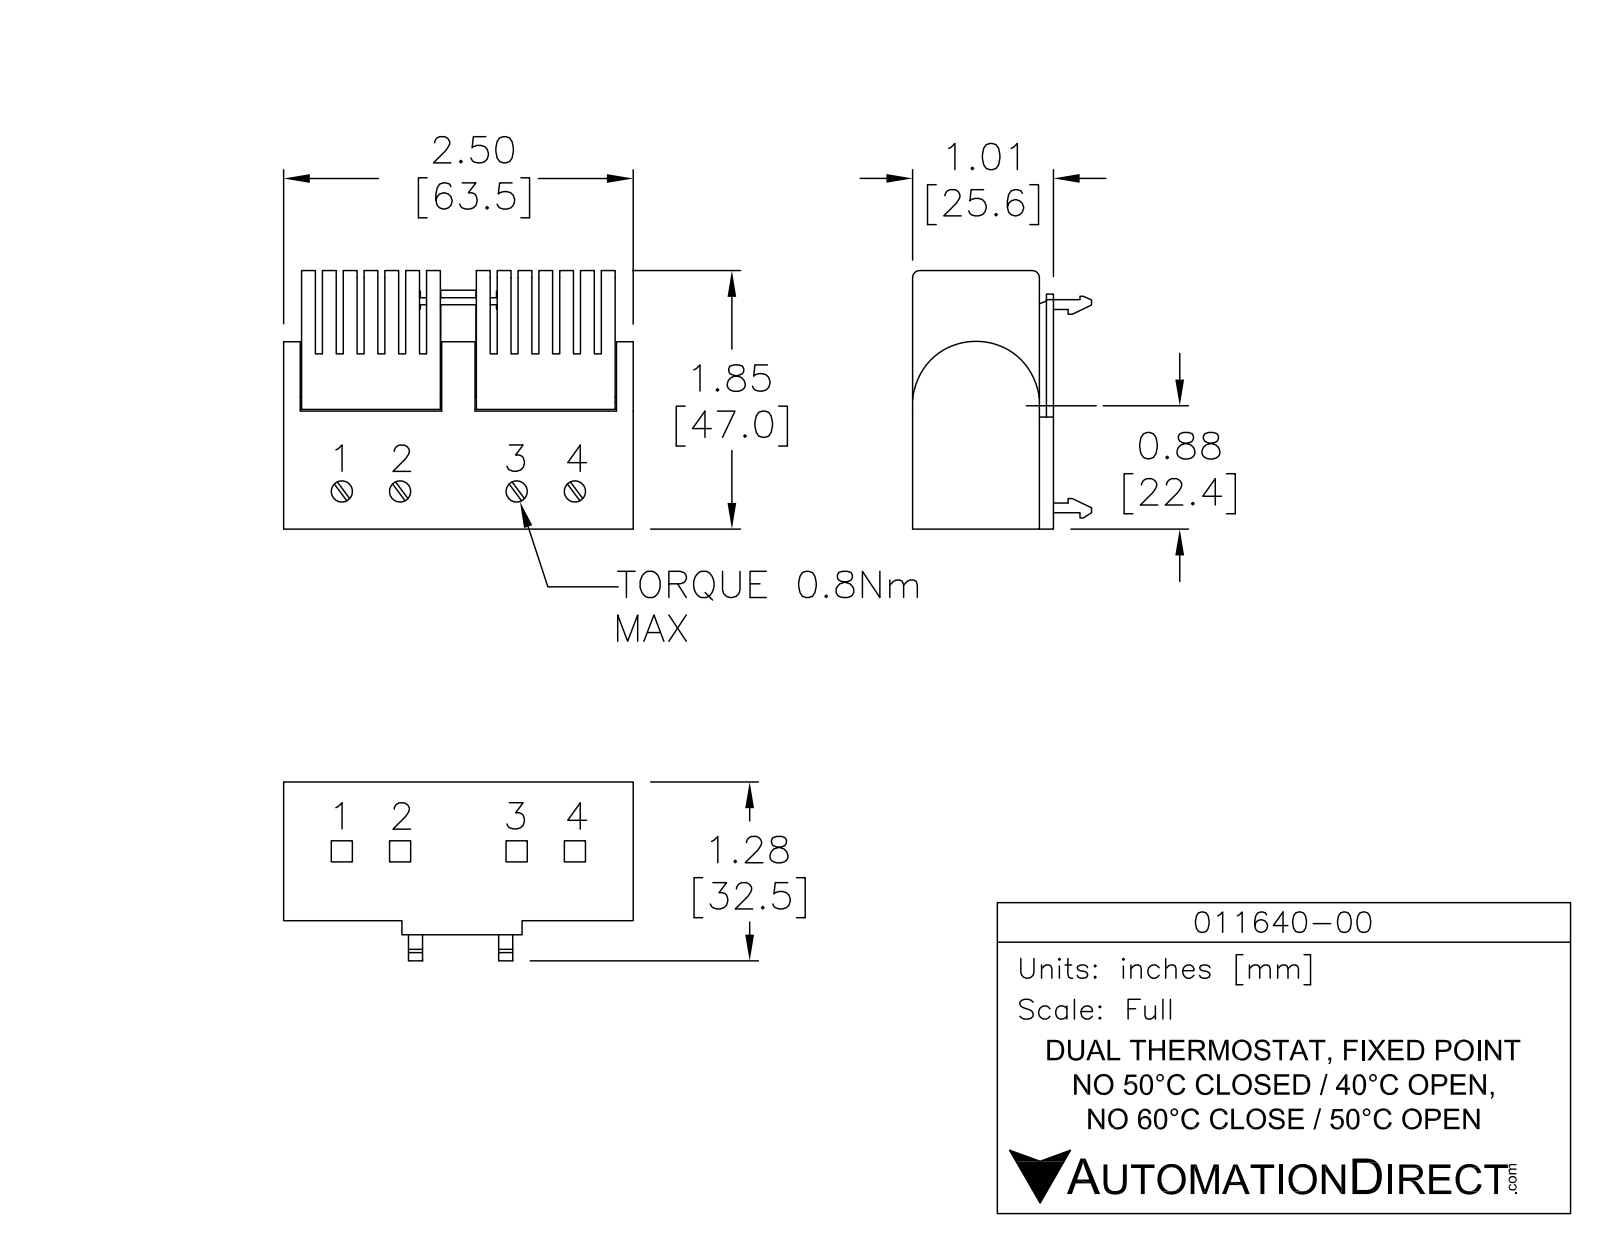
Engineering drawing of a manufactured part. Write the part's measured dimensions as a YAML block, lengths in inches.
part_name: "011640-00"
step_written_by: "SolidWorks 2013 (AUTOMOTIVE_DESIGN)"
units: inches
bodies: {solids: 1, faces: 230, planar: 107, cylindrical: 98, other: 25}
overall_size: [1.821, 1.305, 0.905]
volume: 1.871
surface_area: 12.98
partial_cylinders:
  - {radius: 0.025, count: 16}
  - {radius: 0.023, count: 10}
  - {radius: 0.06, count: 7}
  - {radius: 0.03, count: 6}
  - {radius: 0.04, count: 4}
  - {radius: 0.486, count: 2}
  - {radius: 0.452, count: 1}
face_to_face_distances: [1.305, 0.905, 0.178, 1.127, 0.91, 0.911, 0.14, 0.28, 1.821, 0.185]
